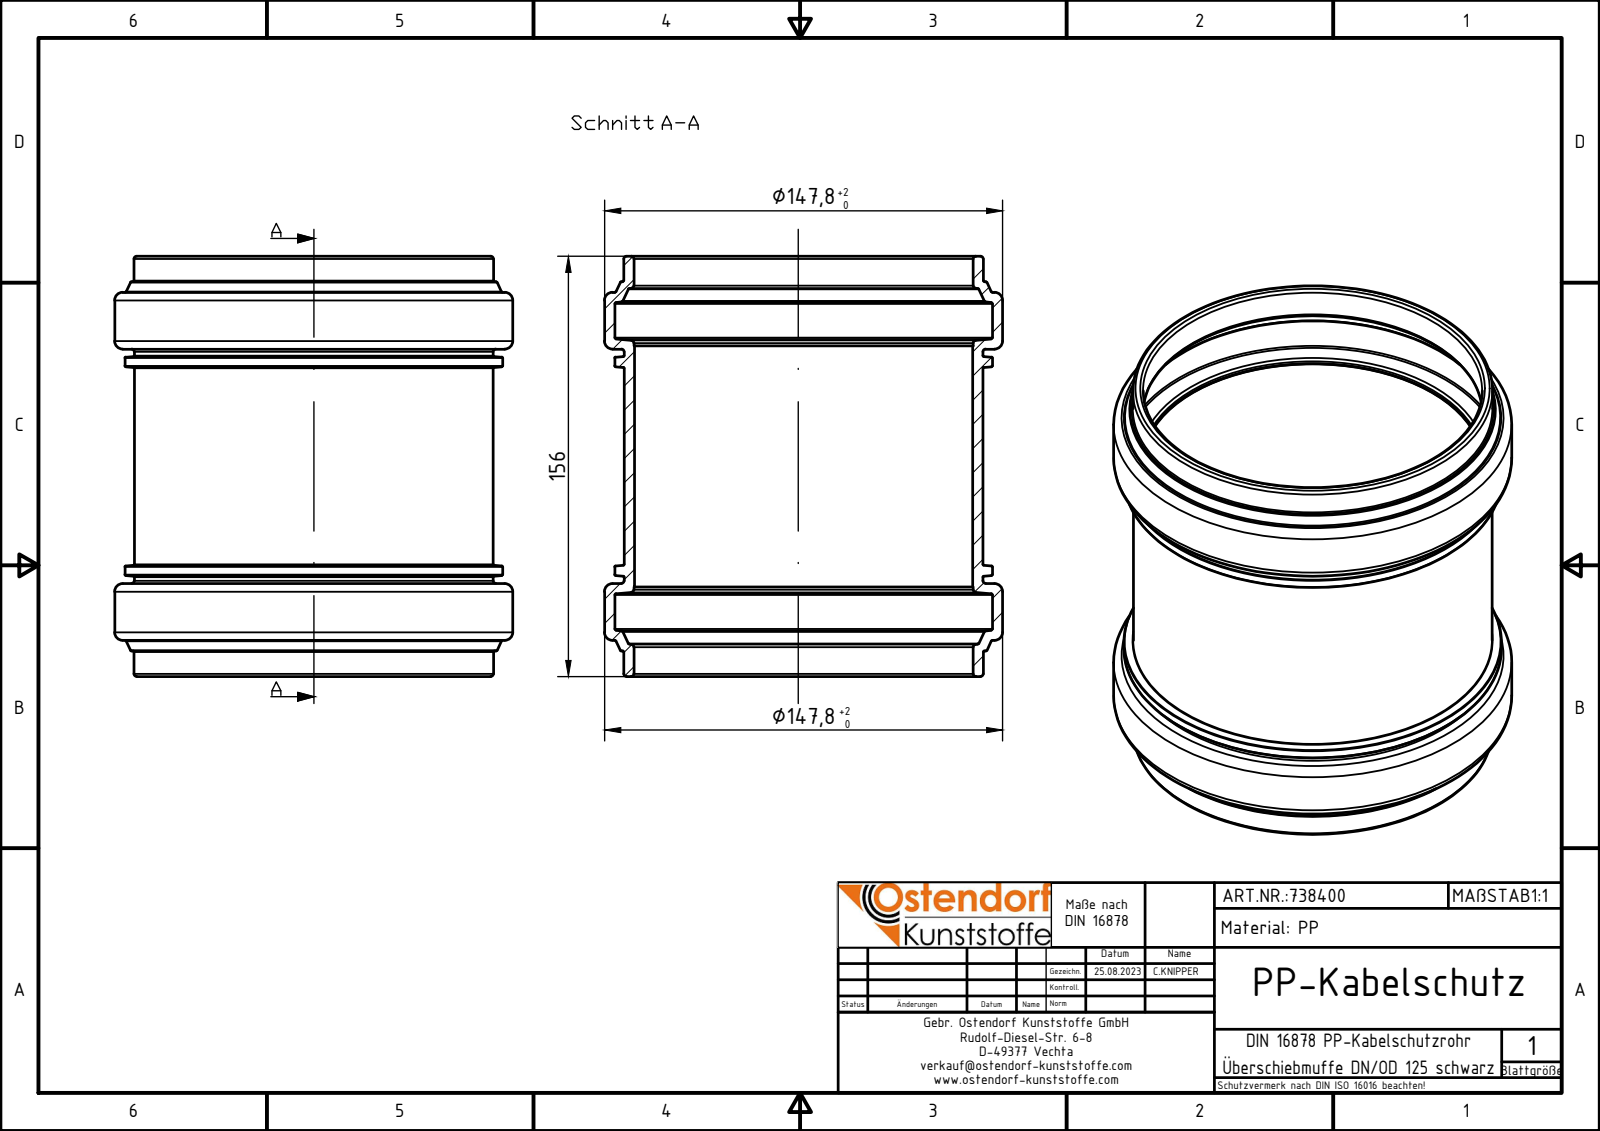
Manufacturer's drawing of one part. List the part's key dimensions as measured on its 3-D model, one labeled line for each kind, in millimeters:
Part name (STEP PRODUCT): 738400z
STEP written by: Autodesk Inventor 2024 (AUTOMOTIVE_DESIGN)
Units: millimetres
Bodies: 1 solid, 76 faces (10 planar, 16 cylindrical, 50 other)
Overall size (bounding box): 156 × 147.8 × 147.8
Volume: 292 695 mm³ · Surface area: 155 392 mm²
Round holes (diameter × count): ⌀125.6 ×1, ⌀125.9 ×1, ⌀140.2 ×1
Round bosses / shafts (diameter × count): ⌀147.8 ×1, ⌀133.5 ×1, ⌀133.2 ×1
Main face-to-face distances: 34.5, 121.5, 87, 156, 13.4, 142.6, 21.1, 108.1, 9.48, 146.52
